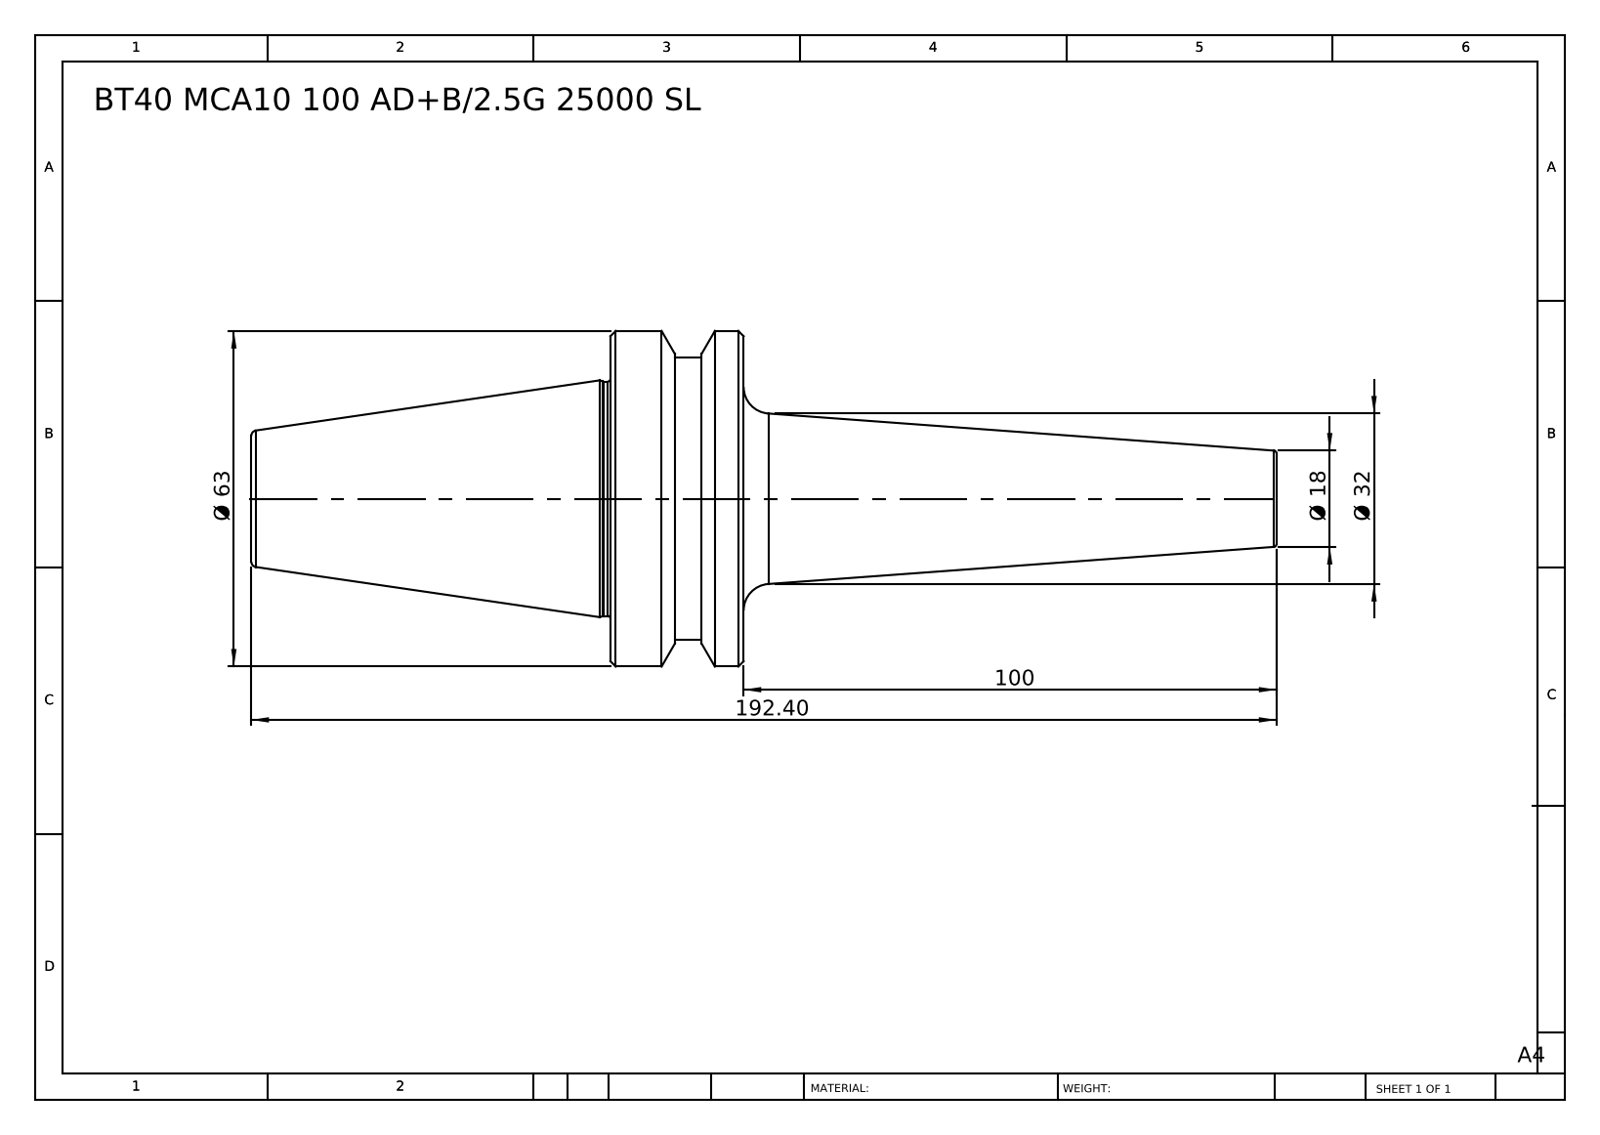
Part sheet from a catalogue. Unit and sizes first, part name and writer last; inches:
Units: inches
Overall size (bounding box): 7.575 × 2.48 × 2.48
Round bosses / shafts (diameter × count): ⌀2.48 ×1, ⌀2.087 ×1, ⌀1.732 ×1
Main face-to-face distances: 0.984, 3.638, 2.654, 3.937, 4.921, 7.575, 4.445, 0.508, 0.476, 3.13
Volume: 11.64 in³ · Surface area: 39.59 in²
Bodies: 1 solid, 38 faces (6 planar, 8 cylindrical, 24 other)
Part name (STEP PRODUCT): BT40 MCA10 100 AD+B-2.5G 25000 SL
STEP written by: SolidWorks 2014 (CONFIG_CONTROL_DESIGN)
